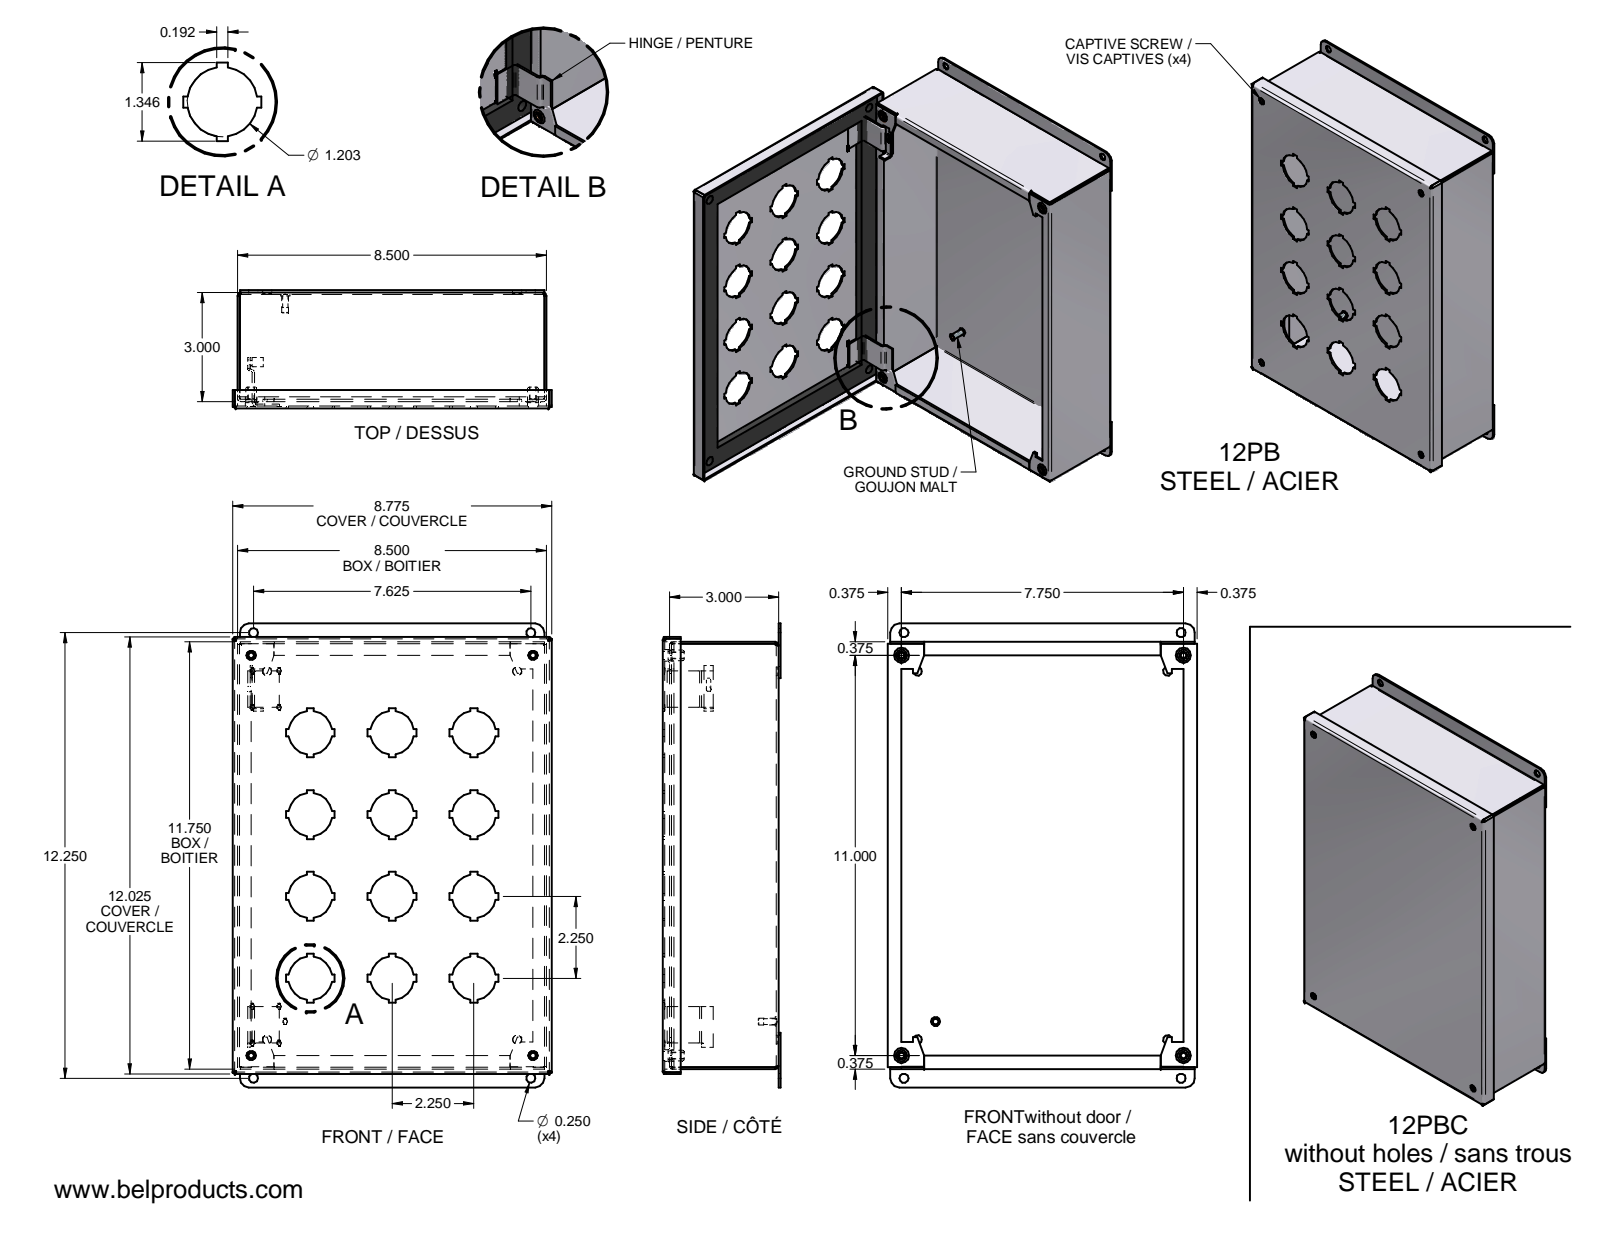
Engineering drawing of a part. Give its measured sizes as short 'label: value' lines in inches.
name: 12PBC_COUVERCLE; 12PBC-C; 12PBC_GASKET; PB-PENTURE-1 (+7 more)
written by: Unknown (AUTOMOTIVE_DESIGN)
unit: in
bodies: 13 solids, 1286 faces (899 planar, 106 cylindrical, 281 other)
size: 12.75 × 8.775 × 3.245
volume: 29.99 in³; area: 855 in²
holes: 9× ⌀0.125, 8× ⌀0.25, 4× ⌀0.159, 4× ⌀0.216, 4× ⌀0.245, 4× ⌀0.265, 4× ⌀0.29, 4× ⌀0.312, 1× ⌀0.136
bosses: 9× ⌀0.119, 4× ⌀0.296, 4× ⌀0.25, 1× ⌀0.256, 1× ⌀0.19, 1× ⌀0.02
rounds: 16× R0.032, 16× R0.092, 4× R0.25, 2× R0.063
face distances: 0.06, 3.125, 3.185, 3.065, 8.44, 11.69, 8.5, 8.38, 0.137, 0.25
hole spacings: 0.628, 10.572, 11.625, 12.847, 11, 0.619, 0.736, 1.01
